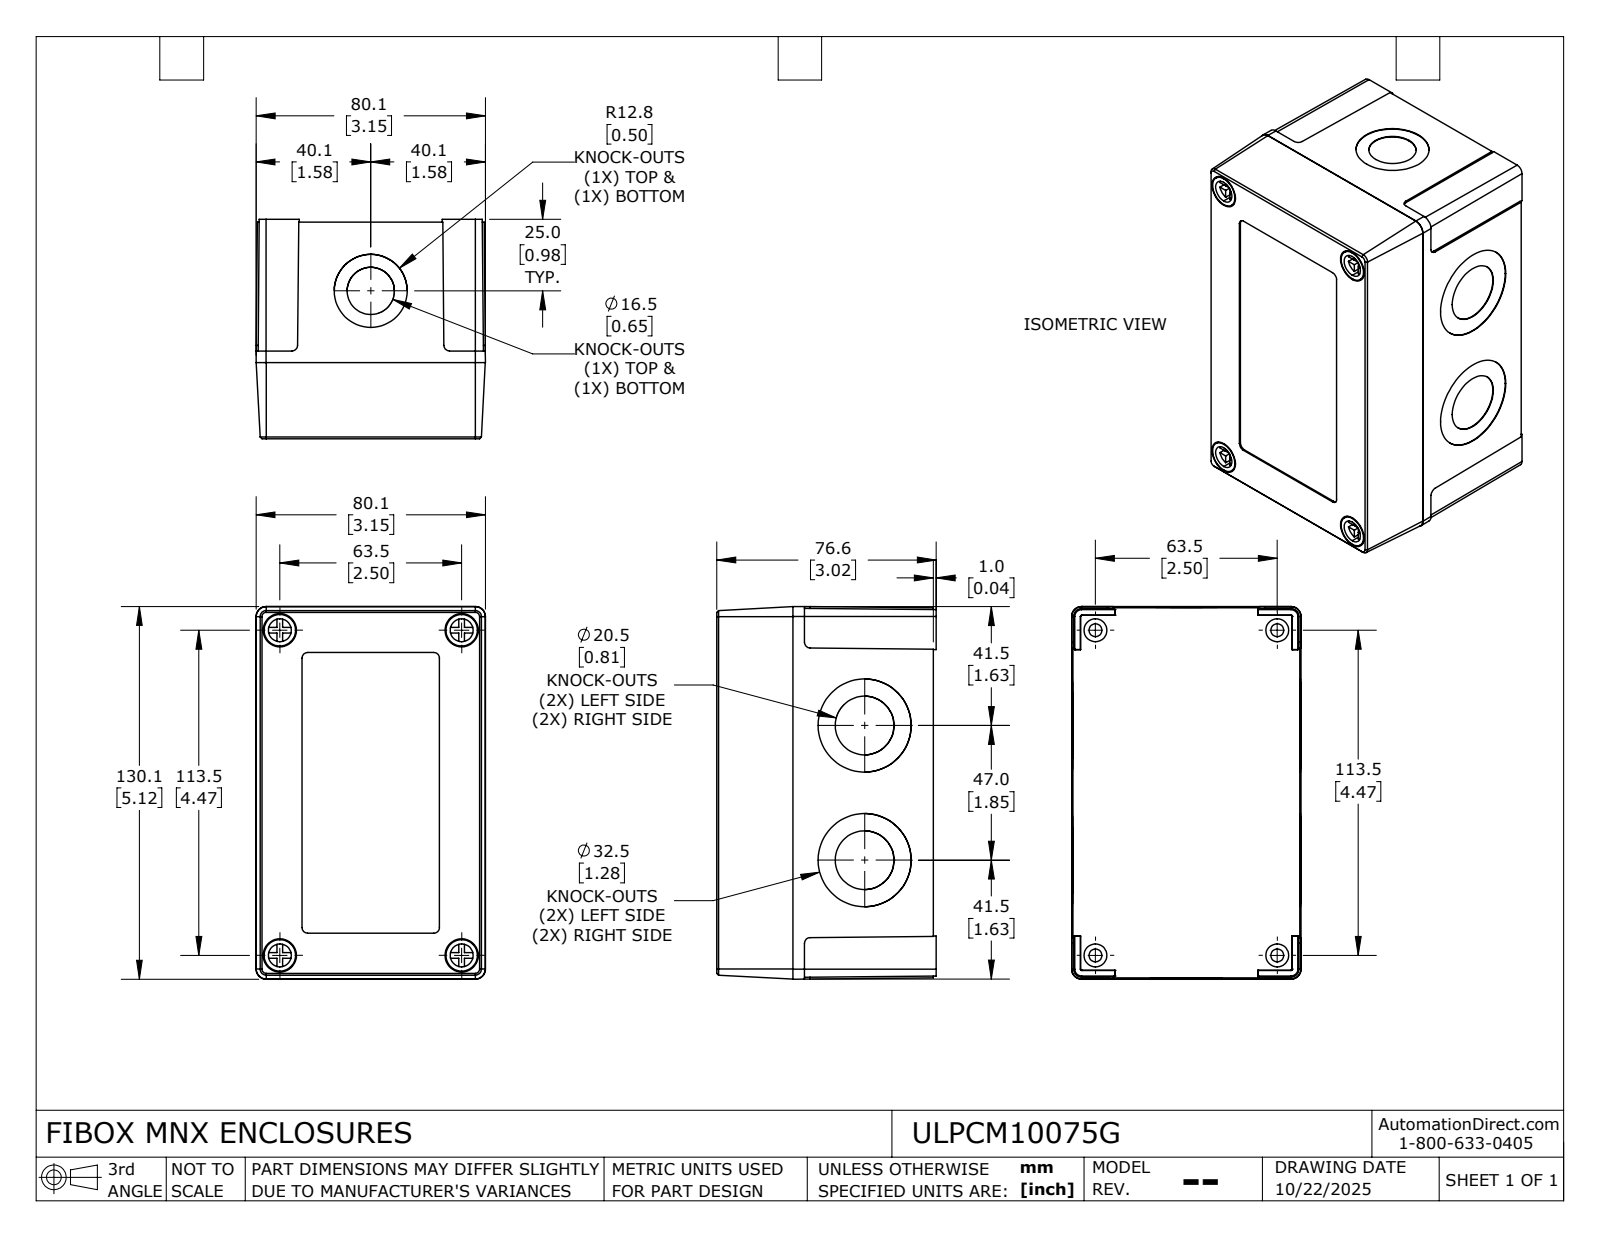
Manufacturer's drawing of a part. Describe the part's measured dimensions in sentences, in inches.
The part is named "ULPCM10075G_Default". Its 3-D file was written by "SolidWorks 2024 (CONFIG_CONTROL_DESIGN)". It is 6 solids with 510 faces: 294 planar, 176 cylindrical and 40 other. Overall it measures 5.122 by 3.154 by 3.016 inches. Its volume is 11.86 cubic inches and its surface area 176.8 square inches. Round holes: 8 of diameter 0.126, 8 of diameter 0.157, 4 of diameter 0.177, 4 of diameter 0.315, 4 of diameter 0.457, 4 of diameter 0.807, 4 of diameter 1.28, 2 of diameter 0.65, 2 of diameter 1.004. Round bosses or shafts: 8 of diameter 0.315, 8 of diameter 0.098, 4 of diameter 0.433, 4 of diameter 0.283. Partial cylindrical surfaces (rounded edges, fillets, slot ends): 8 of radius 0.079, 6 of radius 0.056, 4 of radius 0.021, 4 of radius 0.197, 2 of radius 0.023. The main face-to-face distances are 0.165, 2.878, 0.118, 2.76, 0.079, 2.858, 0.098, 2.839, 0.02, 2.957. The hole center spacings are 0.841, 0.888, 1.333, 1.476, 1.939, 2.159, 2.174, 2.281.
